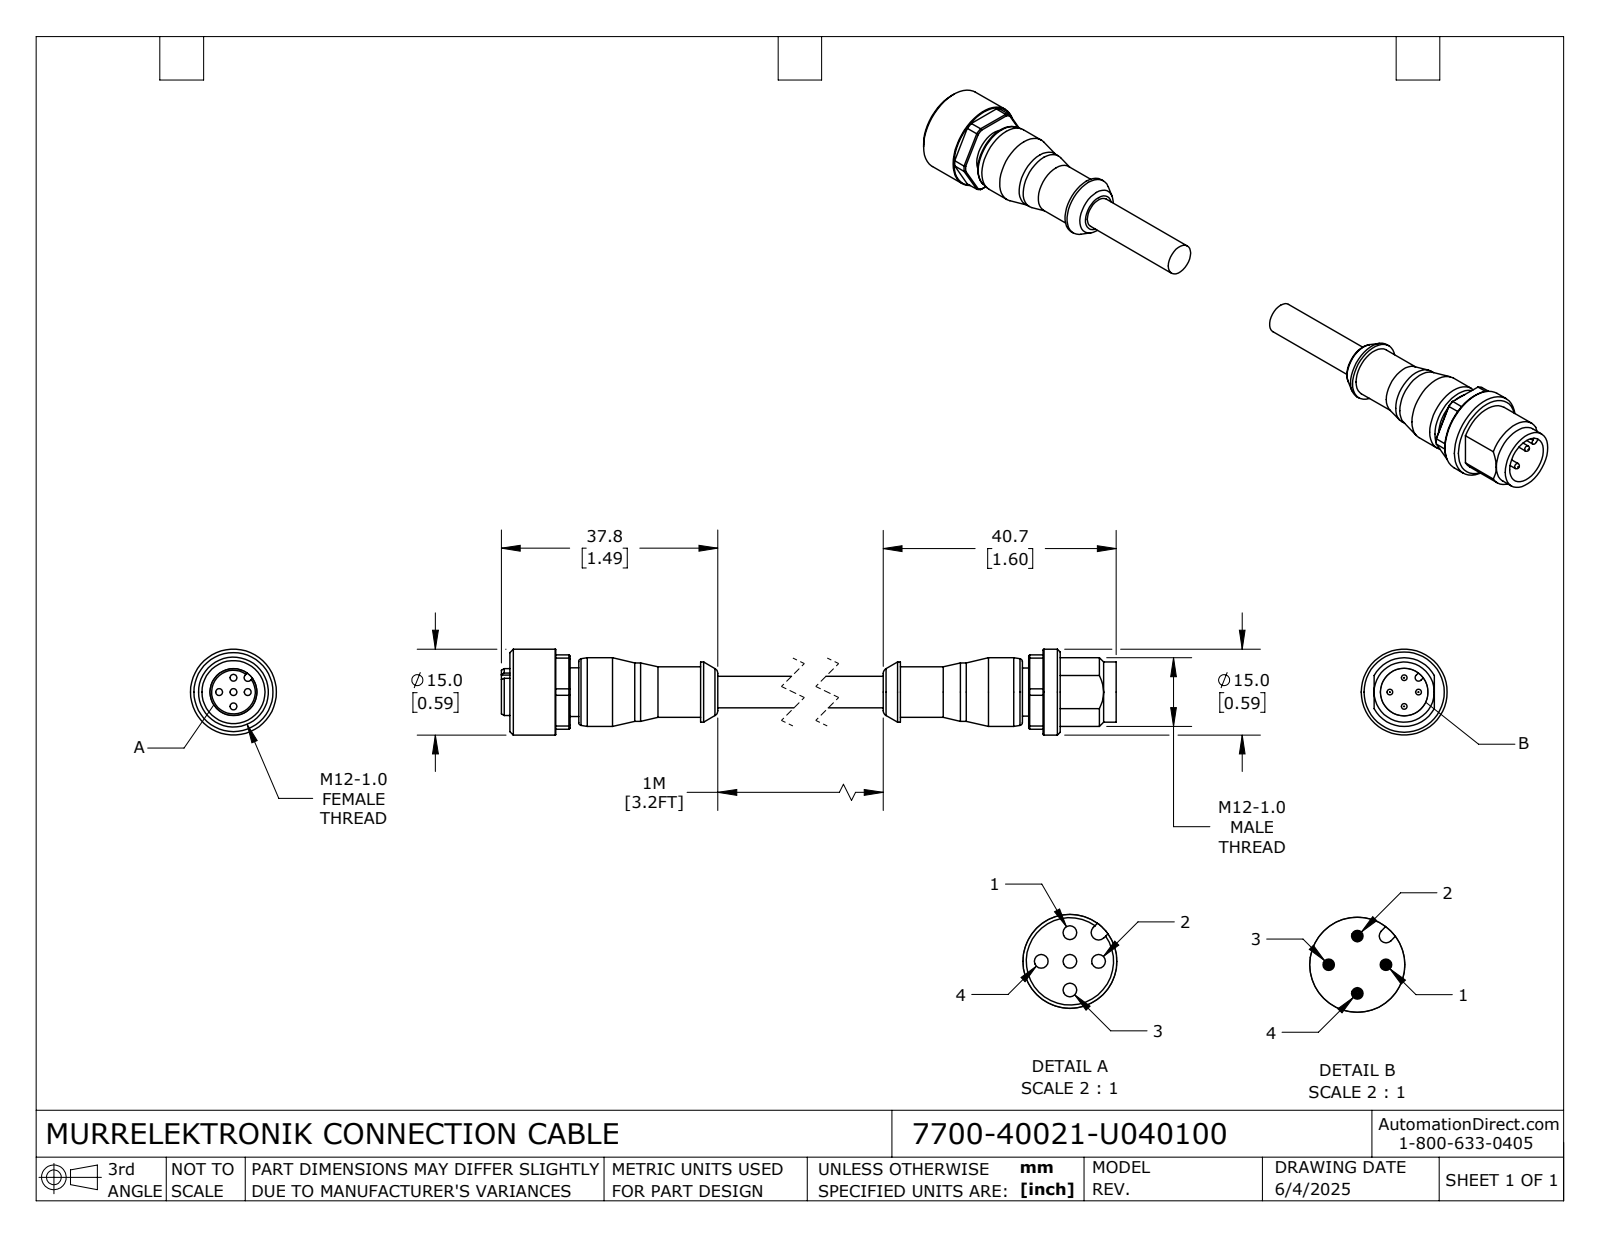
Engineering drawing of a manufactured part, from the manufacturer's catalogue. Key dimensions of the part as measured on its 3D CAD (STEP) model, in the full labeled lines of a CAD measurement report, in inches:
Part name (STEP PRODUCT): 7700-40021-U040100_FEMALE; 7700-40021-U040100_MALE; 7700-40021-U040100
STEP written by: SolidWorks 2024 (CONFIG_CONTROL_DESIGN)
Units: inches
Bodies: 2 solids, 191 faces (59 planar, 71 cylindrical, 61 other)
Overall size (bounding box): 5.65 × 0.591 × 0.591
Volume: 0.487 in³ · Surface area: 7.972 in²
Round holes (diameter × count): ⌀0.047 ×5, ⌀0.327 ×1, ⌀0.433 ×1
Round bosses / shafts (diameter × count): ⌀0.039 ×4, ⌀0.591 ×1, ⌀0.472 ×1, ⌀0.413 ×1, ⌀0.402 ×1, ⌀0.346 ×1, ⌀0.335 ×1, ⌀0.331 ×1
Partial cylindrical surfaces — rounded edges, fillets, slot ends (radius × count): R0.024 ×1, R0.026 ×1, R0.283 ×1
Main face-to-face distances: 0.512, 0.118, 4.575, 0.413, 4.945, 0.472, 4.791, 0.295, 0.059, 0.098
Hole centre spacings: 0.098, 0.139, 0.197
